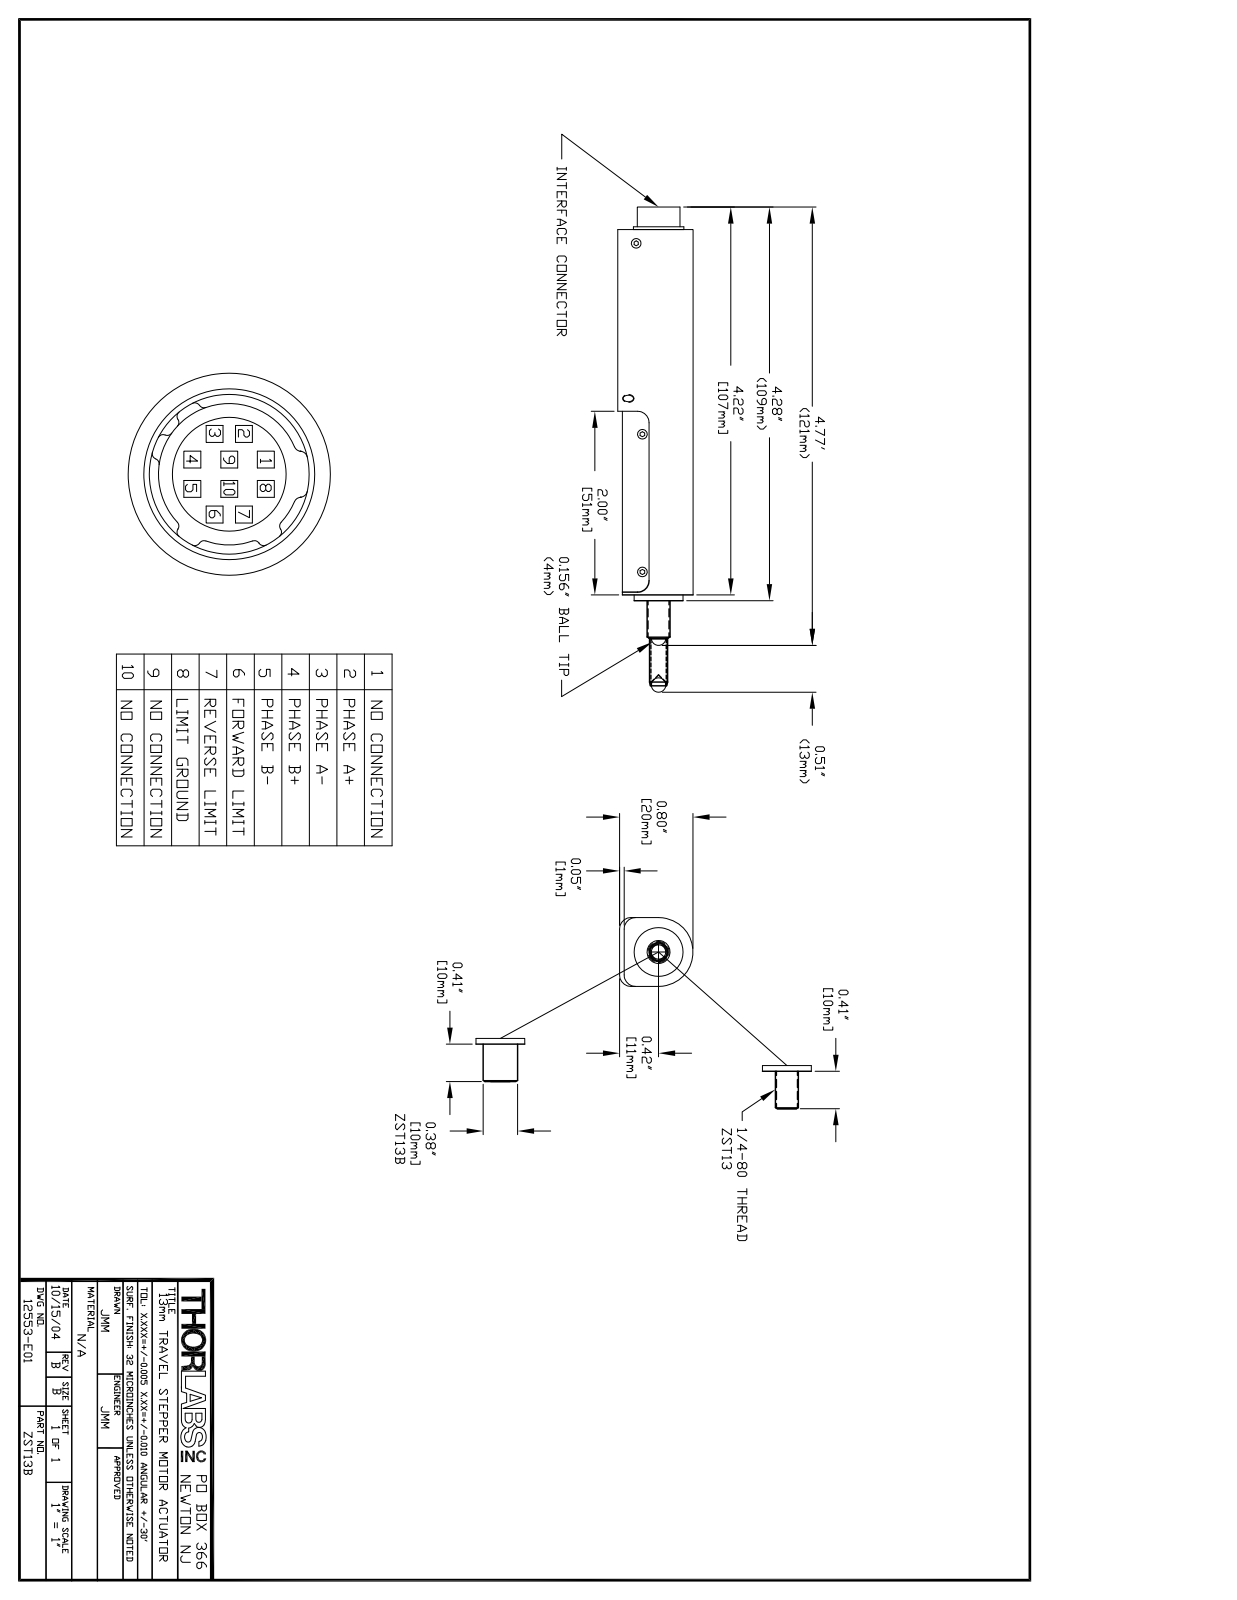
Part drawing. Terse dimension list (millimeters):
name: 12553-E0W
written by: SolidWorks 2007 (AUTOMOTIVE_DESIGN)
unit: mm
bodies: 0 solids, 469 faces (129 planar, 289 cylindrical, 51 other)
size: 135.9 × 21.9 × 21
holes: 10× ⌀1.1, 3× ⌀3.6, 2× ⌀2.2, 1× ⌀4, 1× ⌀9.8
bosses: 6× ⌀3.5, 1× ⌀16, 1× ⌀14, 1× ⌀11.8, 1× ⌀9.5, 1× ⌀7.6, 1× ⌀5
rounds: 6× R3.2, 3× R0.8, 1× R8.7, 1× R8.8, 1× R9.5
face distances: 19.1, 1.3, 0.8, 100.3, 101.1, 102.7, 102, 1.7, 6.6, 7.4
hole spacings: 1.8, 3.5, 2.5, 3.3, 4, 5, 2, 2.6
